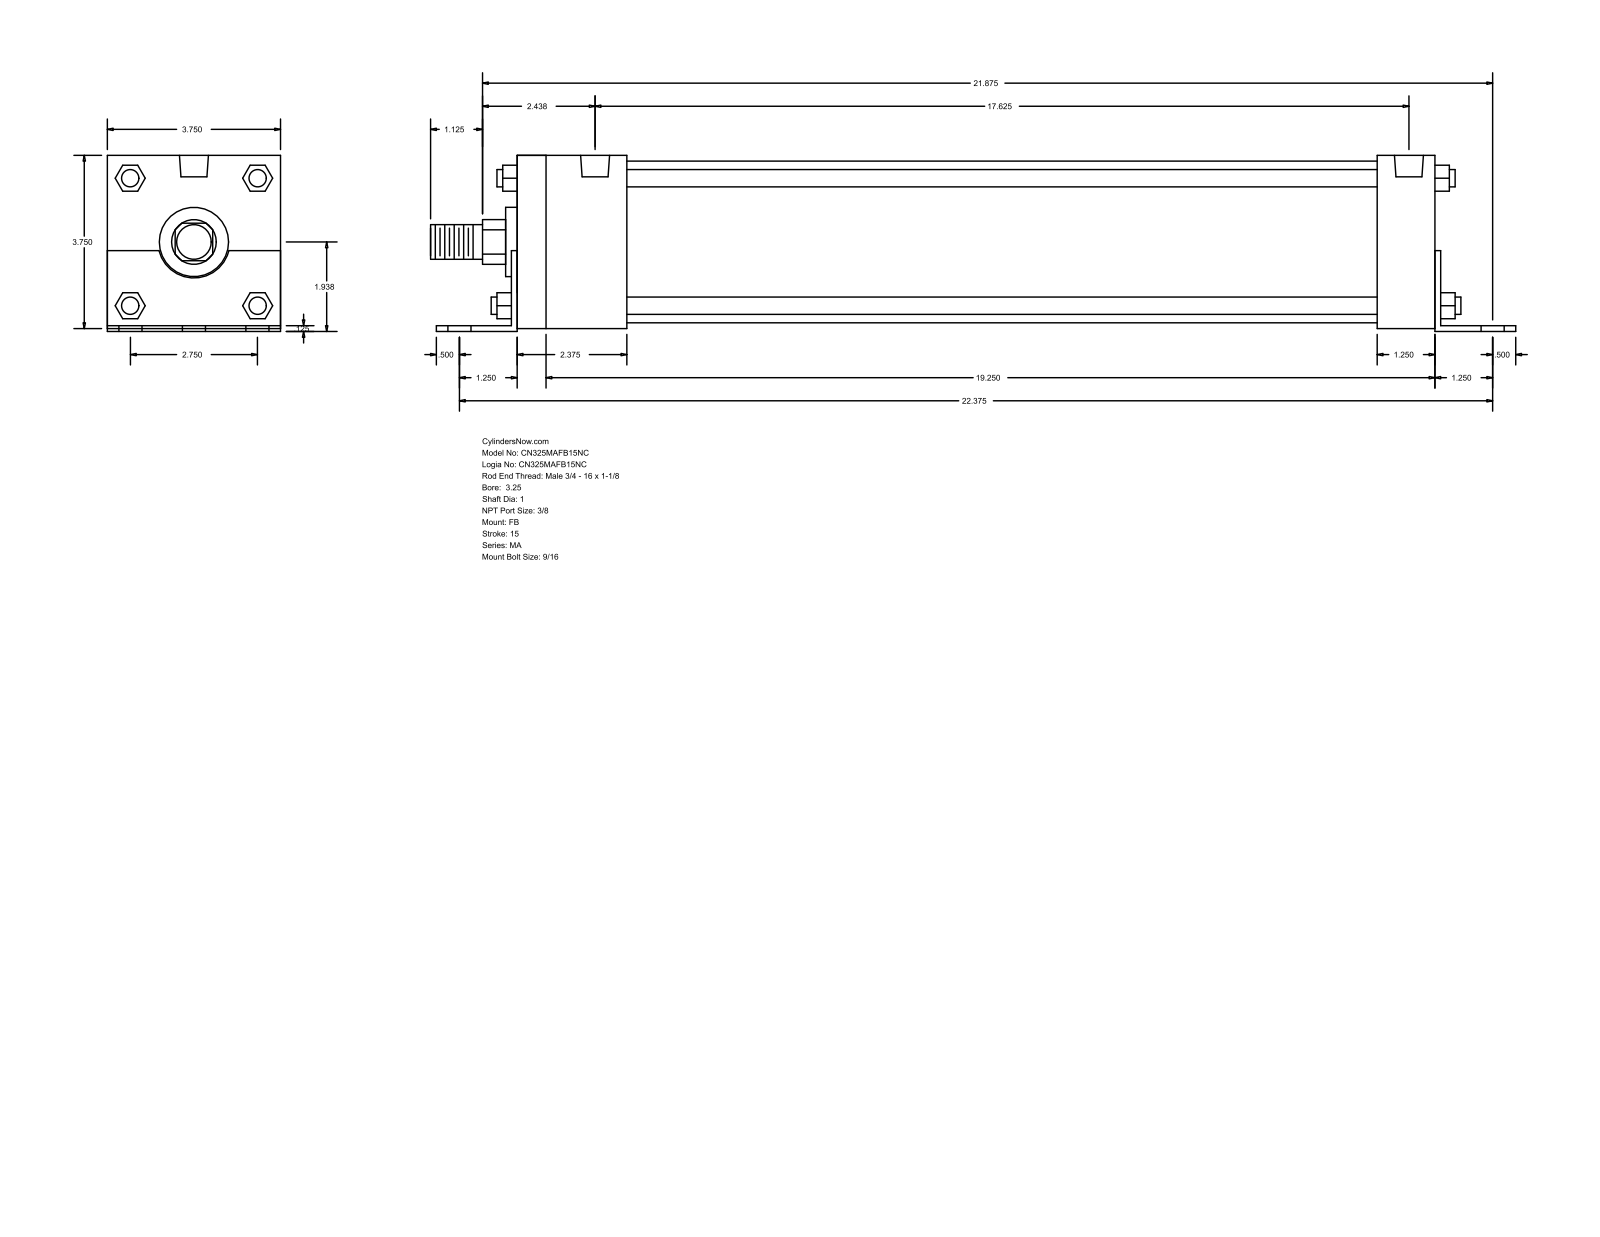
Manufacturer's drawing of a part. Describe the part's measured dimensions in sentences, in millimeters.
The part is named "MA_FB__0325_1". Its 3-D file was written by "GSSL Pune (CONFIG_CONTROL_DESIGN)". It is 0 solids with 140 faces: 105 planar, 35 cylindrical and 0 other. Overall it measures 596.9 by 96.84 by 95.25 millimeters. Round holes: 6 of diameter 14.29, 4 of diameter 11.11, 2 of diameter 15.93. Round bosses or shafts: 4 of diameter 9.53, 1 of diameter 88.9, 1 of diameter 38.1, 1 of diameter 25.4, 1 of diameter 19.05. Partial cylindrical surfaces (rounded edges, fillets, slot ends): 1 of radius 12.29, 1 of radius 19.81. The main face-to-face distances are 95.24, 3.17, 1.59, 96.83, 1.58, 93.66, 508, 504.83, 511.17, 34.93. The hole center spacings are 34.92, 569.39, 568.32, 57.78, 61.64, 69.84, 82.38, 86.71.
